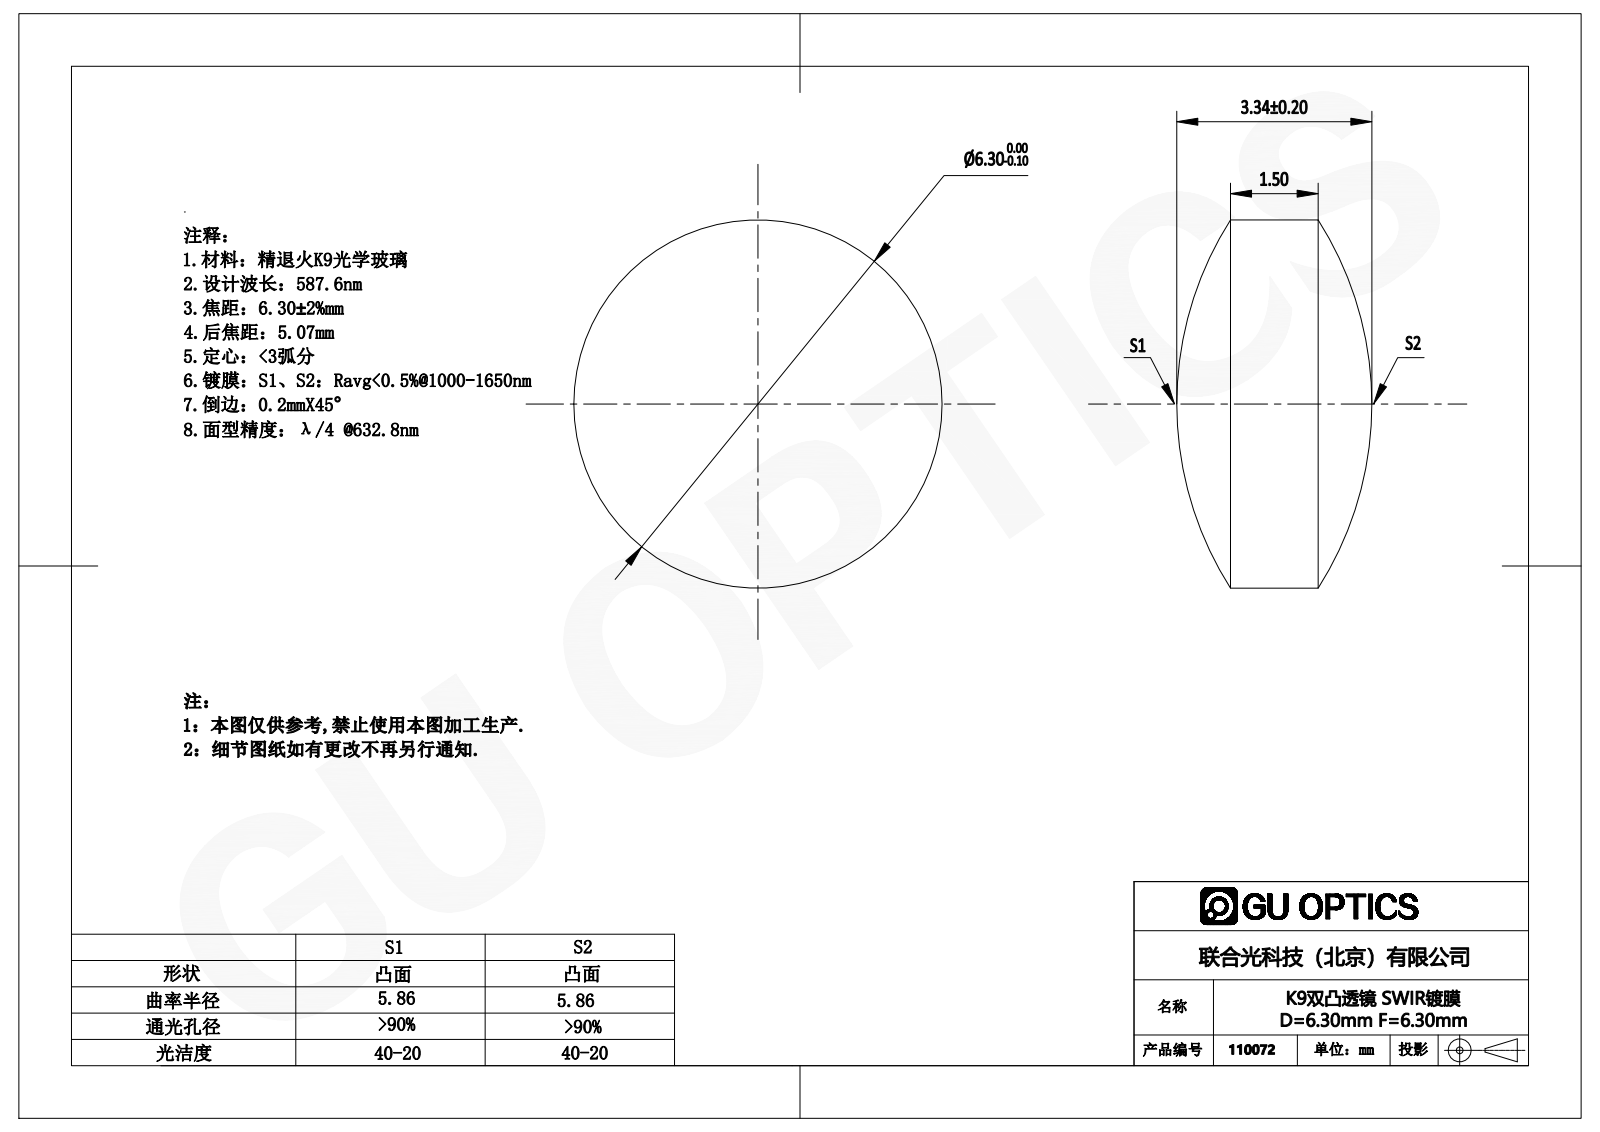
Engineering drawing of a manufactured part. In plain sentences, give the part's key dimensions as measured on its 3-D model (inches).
The part is named "110006". Its 3-D file was written by "SolidWorks 2016 (CONFIG_CONTROL_DESIGN)". It is 1 solid with 6 faces: 0 planar, 2 cylindrical and 4 other. Overall it measures 0.248 by 0.248 by 0.131 inches. Its volume is 0.005 cubic inches and its surface area 0.15 square inches. Round bosses or shafts: 1 of diameter 0.248.
